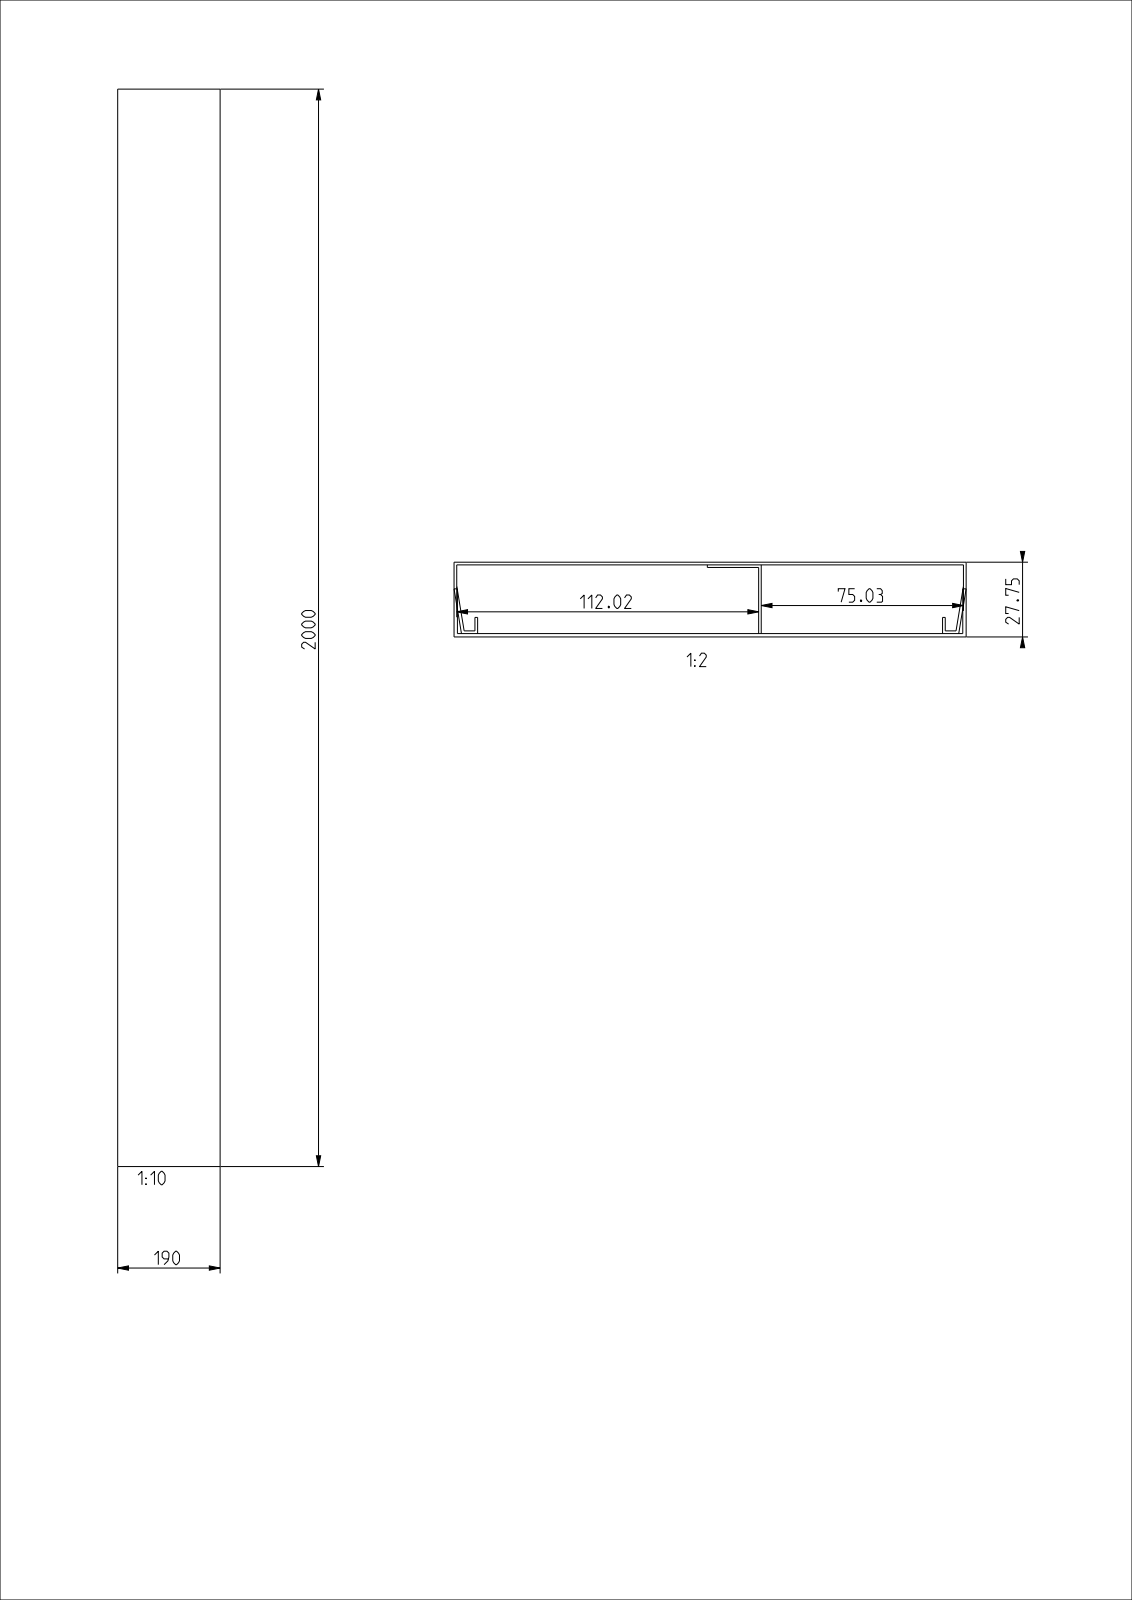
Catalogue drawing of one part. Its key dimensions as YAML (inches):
part_name: "UK190282KUN_OBERTEIL; UK190282KUN_UNTERTEIL; UK190282KUN_ASM"
step_written_by: "CREO PARAMETRIC BY PTC INC, 2022024 (AUTOMOTIVE_DESIGN)"
units: inches
bodies: {solids: 2, faces: 39, planar: 39, cylindrical: 0, other: 0}
overall_size: [78.74, 7.48, 1.093]
volume: 71.76
surface_area: 3179
face_to_face_distances: [0.049, 0.039, 1.043, 1.093, 1.004, 1.053, 7.431, 7.48, 4.487, 2.993]
